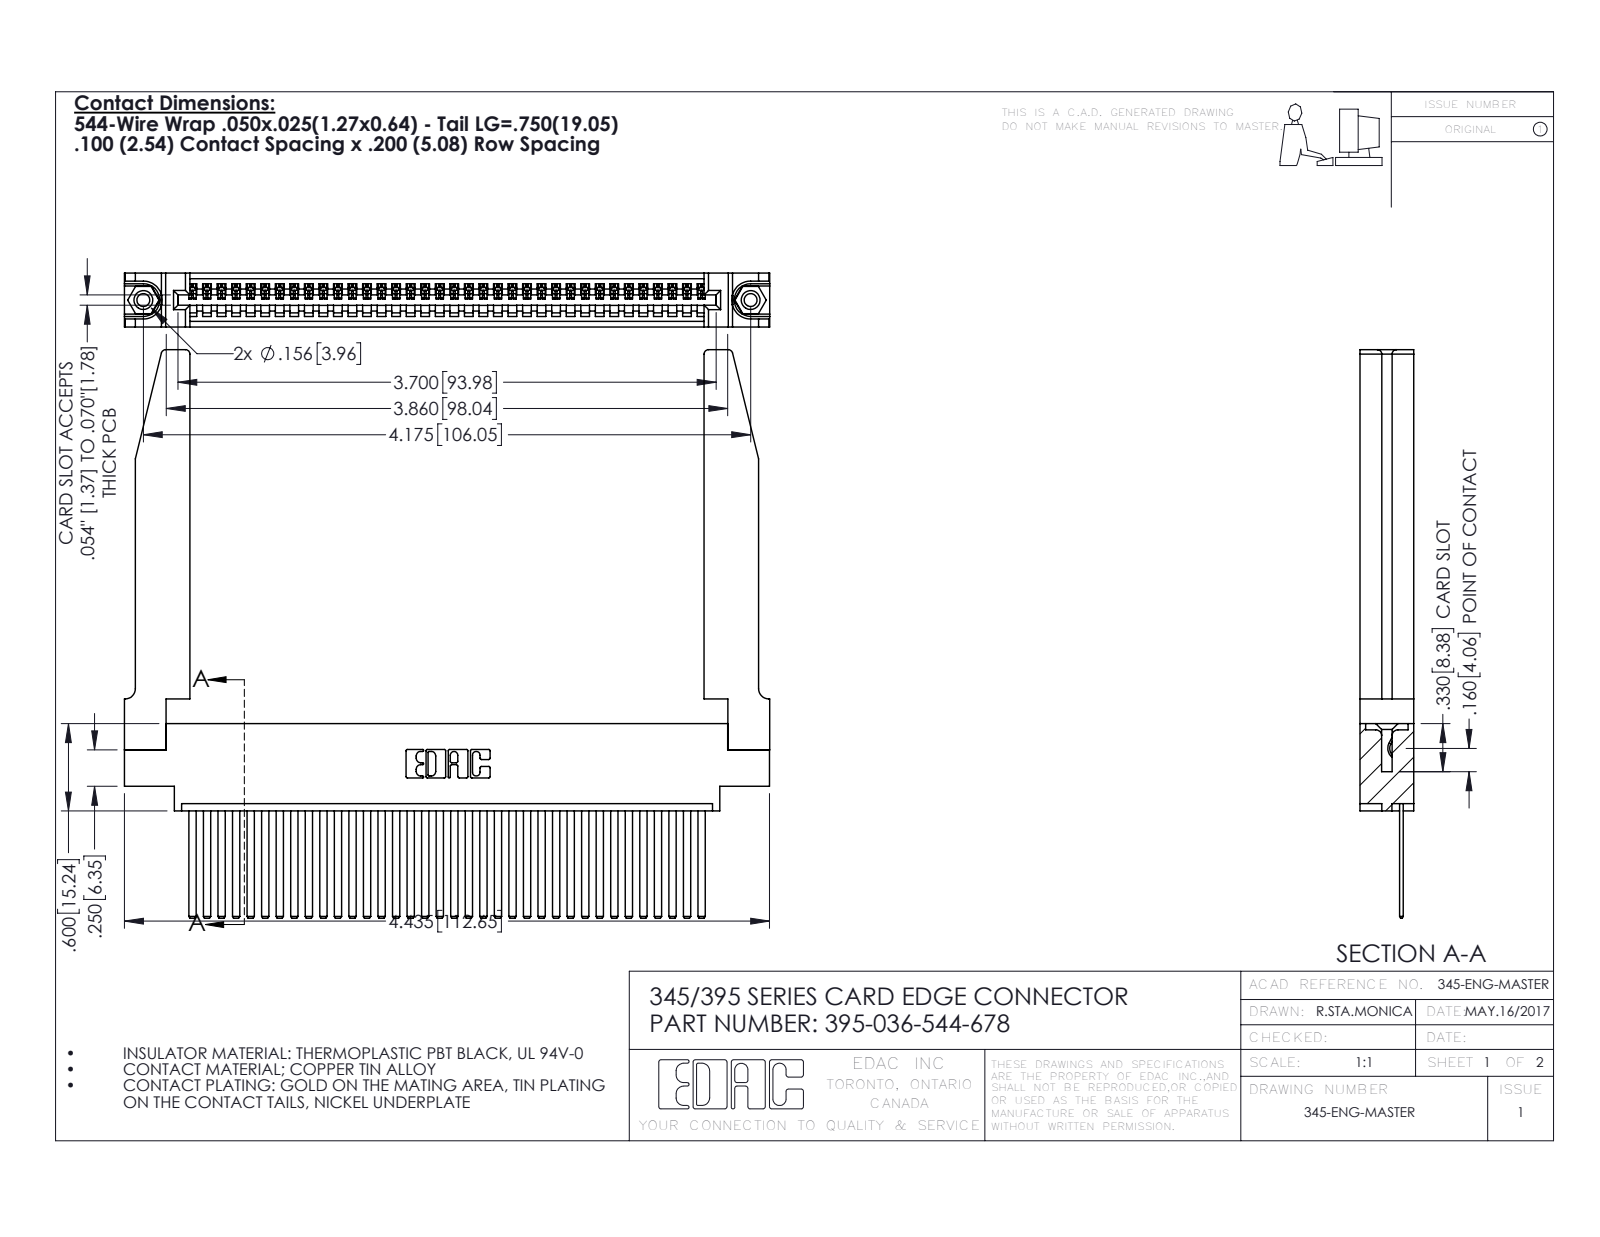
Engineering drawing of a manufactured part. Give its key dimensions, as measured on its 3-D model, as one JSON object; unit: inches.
{"part_name": "345 Part_0.170 Offset - 0.156 Dia-TH; 395-036-544-678; 345-250-001_345-250-001-102; 345-220-078_345-220-078 (+1 more)", "step_written_by": "SolidWorks 2016 (CONFIG_CONTROL_DESIGN)", "units": "inches", "bodies": {"solids": 41, "faces": 2236, "planar": 1522, "cylindrical": 662, "other": 52}, "overall_size": [4.436, 3.907, 0.37], "volume_in3": 1.143, "surface_area_in2": 35.19, "round_holes": [[0.089, 2], [0.125, 2], [0.156, 2], [0.064, 1]], "round_bosses_or_shafts": [[0.155, 2]], "partial_cylinders_radius": [[0.006, 72], [0.01, 22], [0.03, 8], [0.007, 6], [0.031, 6], [0.026, 3], [0.031, 2], [0.04, 2]], "face_to_face_distances": [0.072, 0.37, 0.298, 0.098, 0.272, 0.025, 0.2, 0.225, 0.148, 0.15], "hole_center_spacings": [0.27, 3.939, 4.175]}
